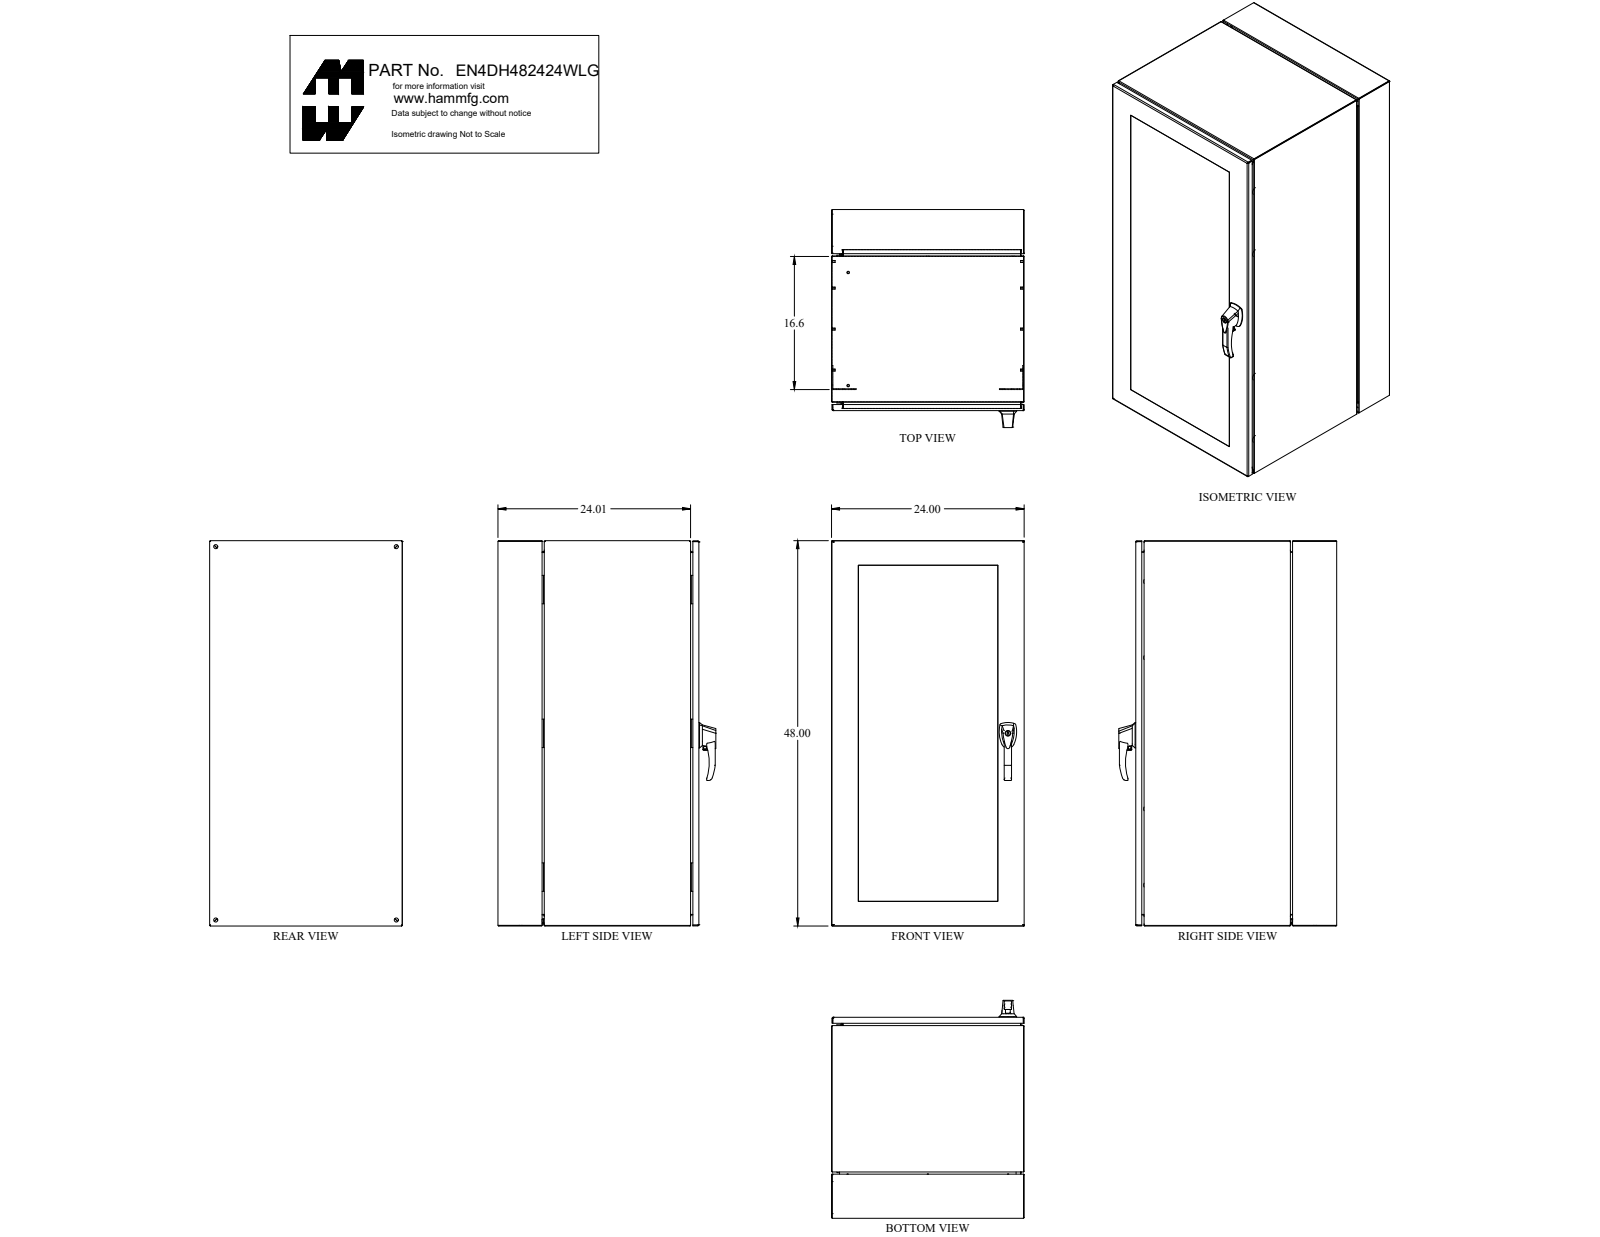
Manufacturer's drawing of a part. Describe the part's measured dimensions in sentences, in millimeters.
The part is named "EN4DH482424WLG". Its 3-D file was written by "SolidWorks 2019 (CONFIG_CONTROL_DESIGN)". It is 291 solids with 5490 faces: 2969 planar, 1459 cylindrical and 1062 other. Overall it measures 1219.2 by 689.8 by 609.6 millimeters. Its volume is 12 580 000 cubic millimeters and its surface area 10 430 000 square millimeters. Round holes: 156 of diameter 4.5, 50 of diameter 3.2, 47 of diameter 6.4, 26 of diameter 3.3, 19 of diameter 5, 14 of diameter 4.8, 14 of diameter 4.9, 14 of diameter 6, 9 of diameter 6.5, 9 of diameter 7, 9 of diameter 7.1, 8 of diameter 4.4. Round bosses or shafts: 30 of diameter 6.4, 26 of diameter 9.3, 26 of diameter 8, 24 of diameter 5.7, 24 of diameter 4.2, 16 of diameter 6, 14 of diameter 12, 14 of diameter 11. Partial cylindrical surfaces (rounded edges, fillets, slot ends): 37 of radius 3.2, 33 of radius 0.9, 33 of radius 2.7, 26 of radius 6.4, 25 of radius 12.7, 24 of radius 1.5, 20 of radius 3.1, 16 of radius 2. The main face-to-face distances are 1.8, 607.8, 605.9, 2.4, 634.3, 636.1, 609.6, 1217.4, 6.4, 627.9. The hole center spacings are 539.8, 25, 454.8, 454.8, 639.8, 343.5, 384.2, 454.8.
